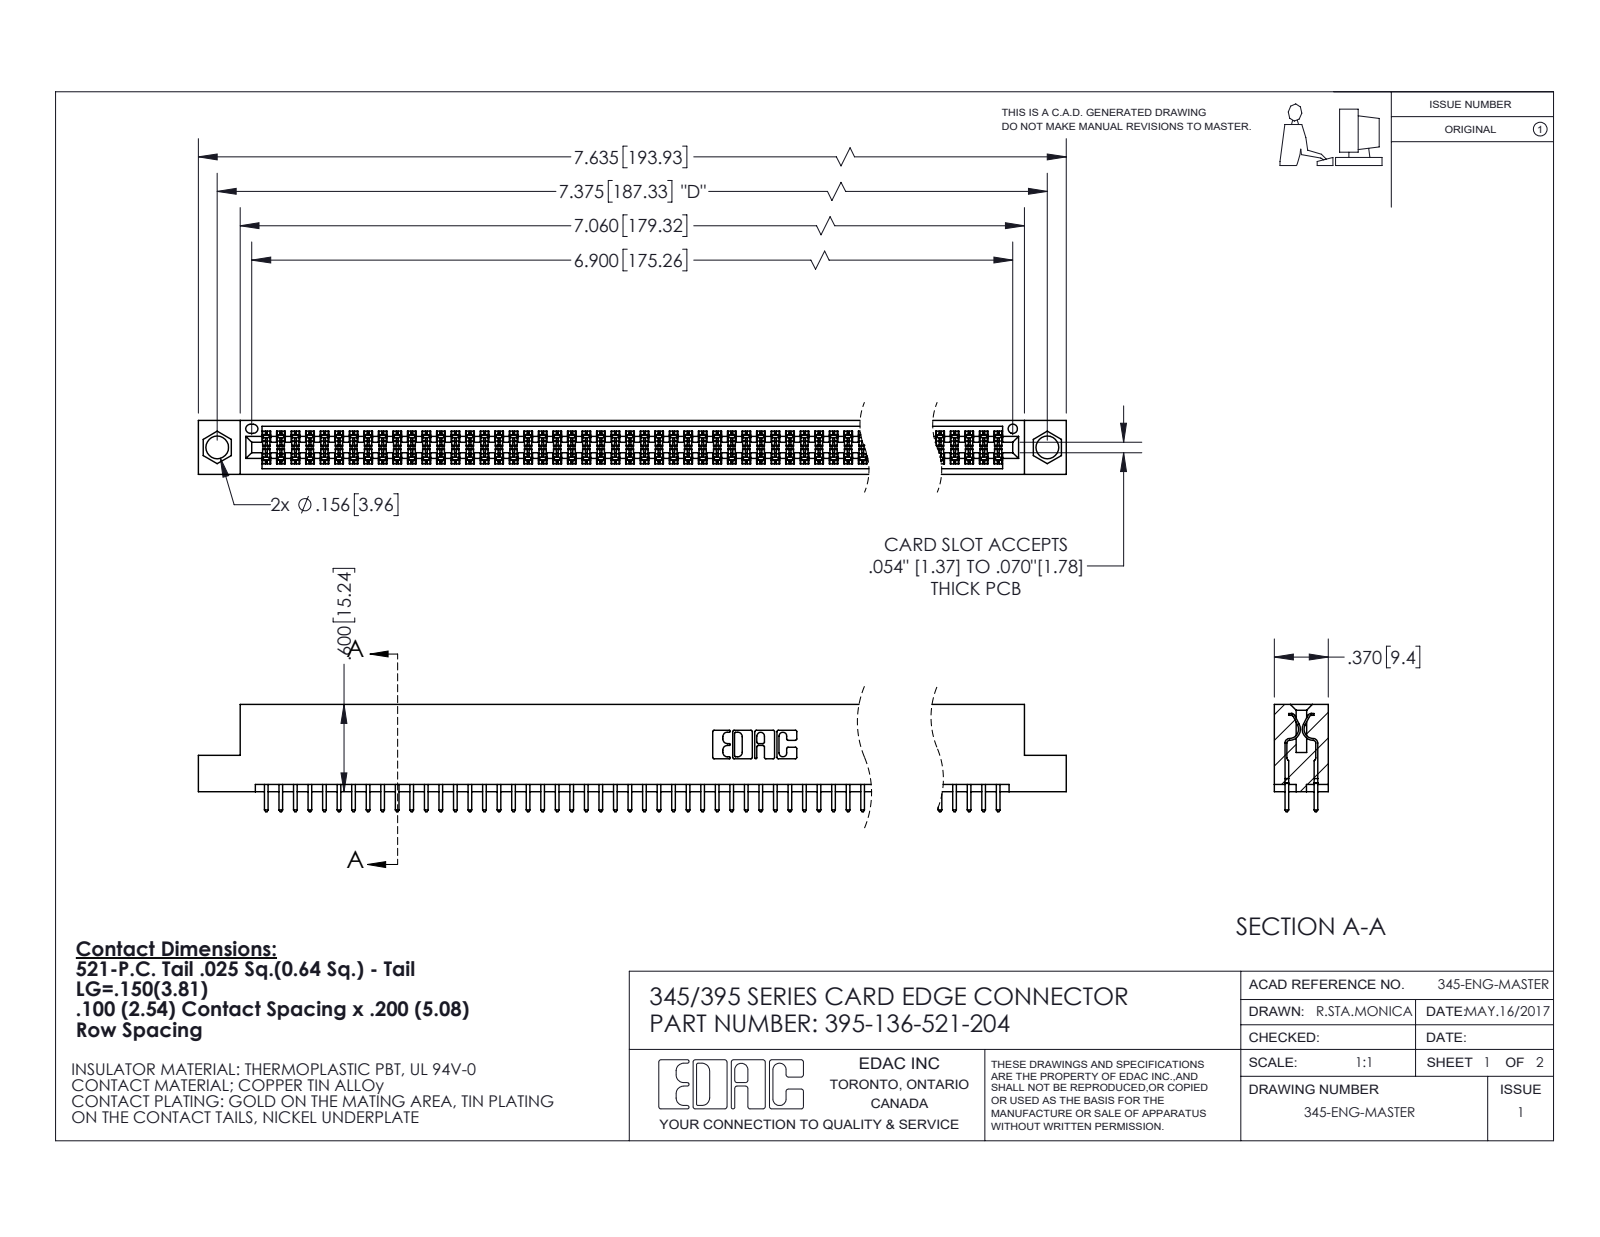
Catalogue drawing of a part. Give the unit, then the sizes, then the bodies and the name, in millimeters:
Units: millimetres
Overall size (bounding box): 193.9 × 18.7 × 9.4
Round holes (diameter × count): ⌀4 ×2, ⌀1.6 ×1
Partial cylindrical surfaces — rounded edges, fillets, slot ends (radius × count): R0.2 ×204, R0.3 ×136, R0.3 ×22, R0.2 ×6, R0.8 ×6, R0.7 ×3, R0.4 ×2, R0.5 ×2
Main face-to-face distances: 1.8, 7.6, 5.1, 2.5, 6.9, 0.6, 9.4, 5.7, 4.4, 3.8
Hole centre spacings: 6.9, 181.3, 187.3
Volume: 18 910 mm³ · Surface area: 27 960 mm²
Bodies: 137 solids, 6940 faces (4582 planar, 2358 cylindrical, 0 other)
Part name (STEP PRODUCT): 345 Part_Flush Mounting Lugs - 0.156 Dia-TI; 345-292-001_345-293-121; 395-136-521-204
STEP written by: SolidWorks 2020 (CONFIG_CONTROL_DESIGN)
